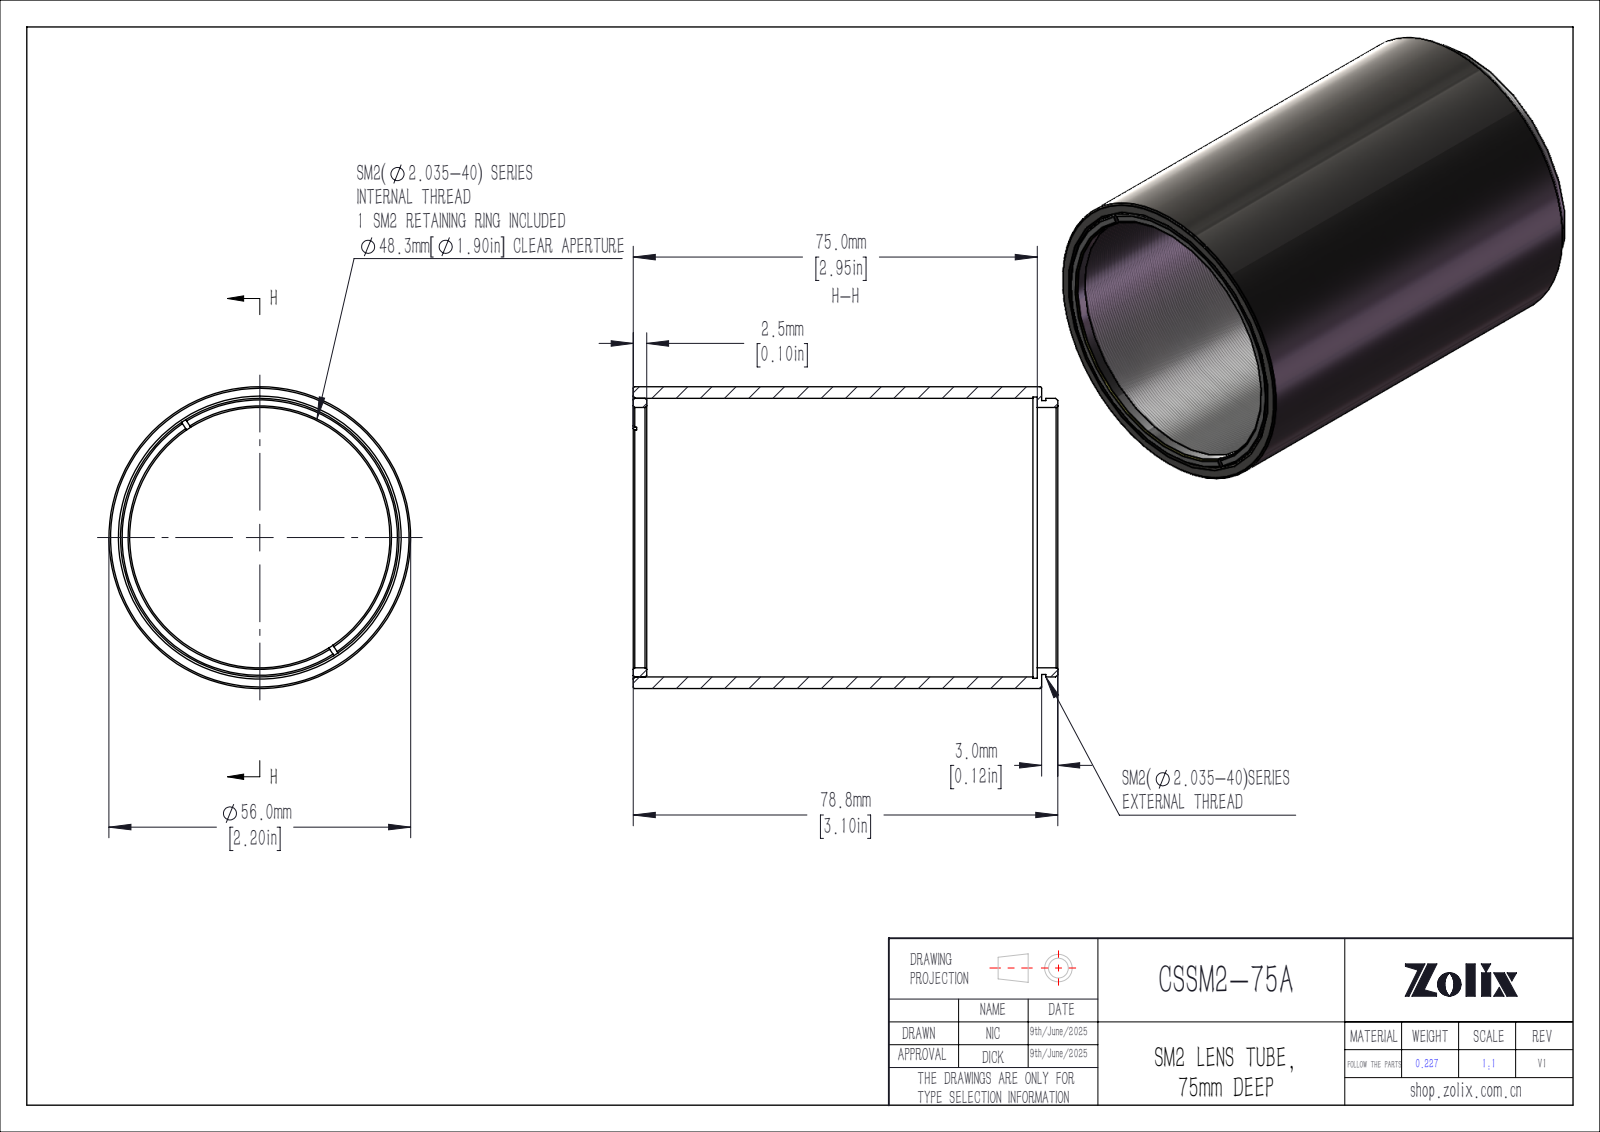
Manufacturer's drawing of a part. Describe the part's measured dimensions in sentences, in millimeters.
The part is named "CSSM2-75A". Its 3-D file was written by "SolidWorks 2020 (CONFIG_CONTROL_DESIGN)". It is 2 solids with 352 faces: 58 planar, 36 cylindrical and 258 other. Overall it measures 78.8 by 56 by 56 millimeters. Its volume is 29 152 cubic millimeters and its surface area 29 137 square millimeters. Round holes: 1 of diameter 48.3, 1 of diameter 52.2. Round bosses or shafts: 1 of diameter 56, 1 of diameter 51.69, 1 of diameter 50.8. Partial cylindrical surfaces (rounded edges, fillets, slot ends): 1 of radius 27.98. The main face-to-face distances are 0.8, 75.8, 75, 2.5, 72.5, 73.3, 78.8, 76.3, 3.8, 3.
